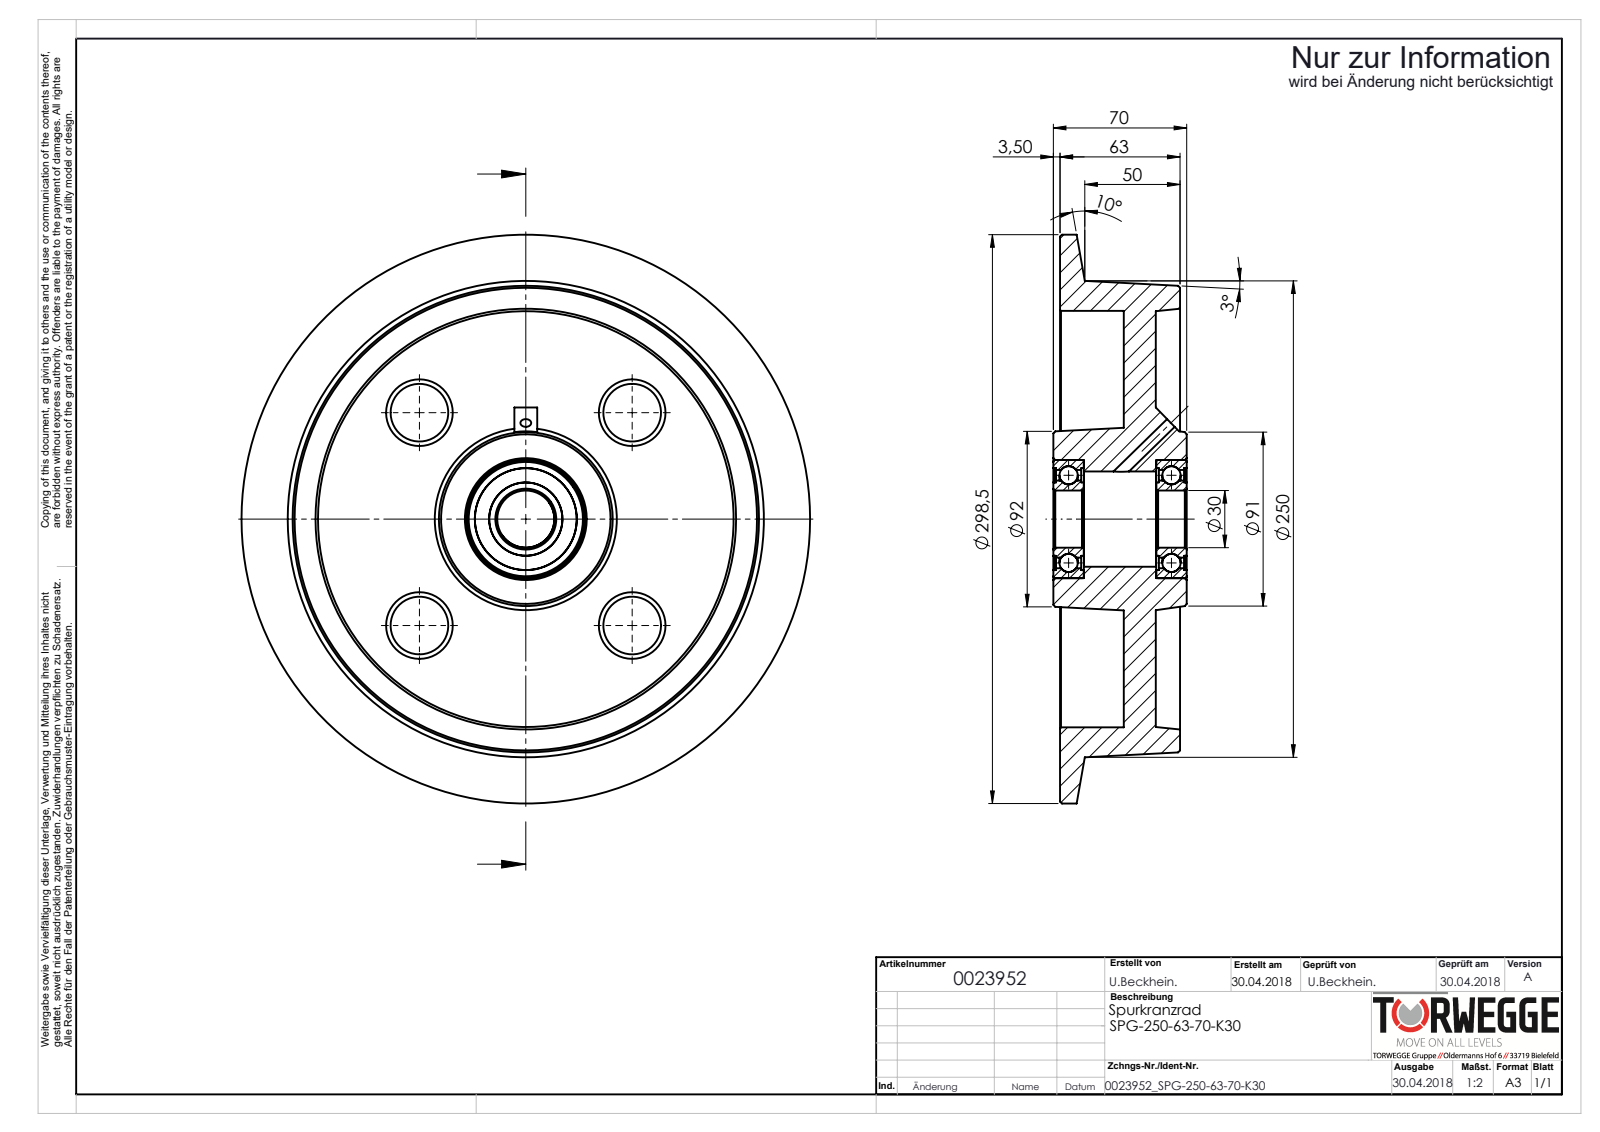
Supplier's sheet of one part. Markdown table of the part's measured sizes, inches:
| quantity | value |
| --- | --- |
| part name | 0023952_SPG-250-63-70-K30 |
| STEP written by | SolidWorks 2018 (AUTOMOTIVE_DESIGN) |
| units | inches |
| bodies | 9 solids, 95 faces (33 planar, 32 cylindrical, 30 other) |
| overall size | 11.752 × 11.752 × 2.756 |
| volume | 105.6 in³ |
| surface area | 436.3 in² |
| round holes (diameter × count) | 0.224 × 1, 1.181 × 1, 1.969 × 1, 2.03 × 1, 2.107 × 1, 2.441 × 1, 8.604 × 1 |
| round bosses / shafts (diameter × count) | 11.752 × 1, 1.592 × 1, 1.515 × 1 |
| main face-to-face distances | 1.318, 1.979, 0.661, 0.138, 2.618, 2.48, 1.163, 0.501, 2.126, 0.63 |
